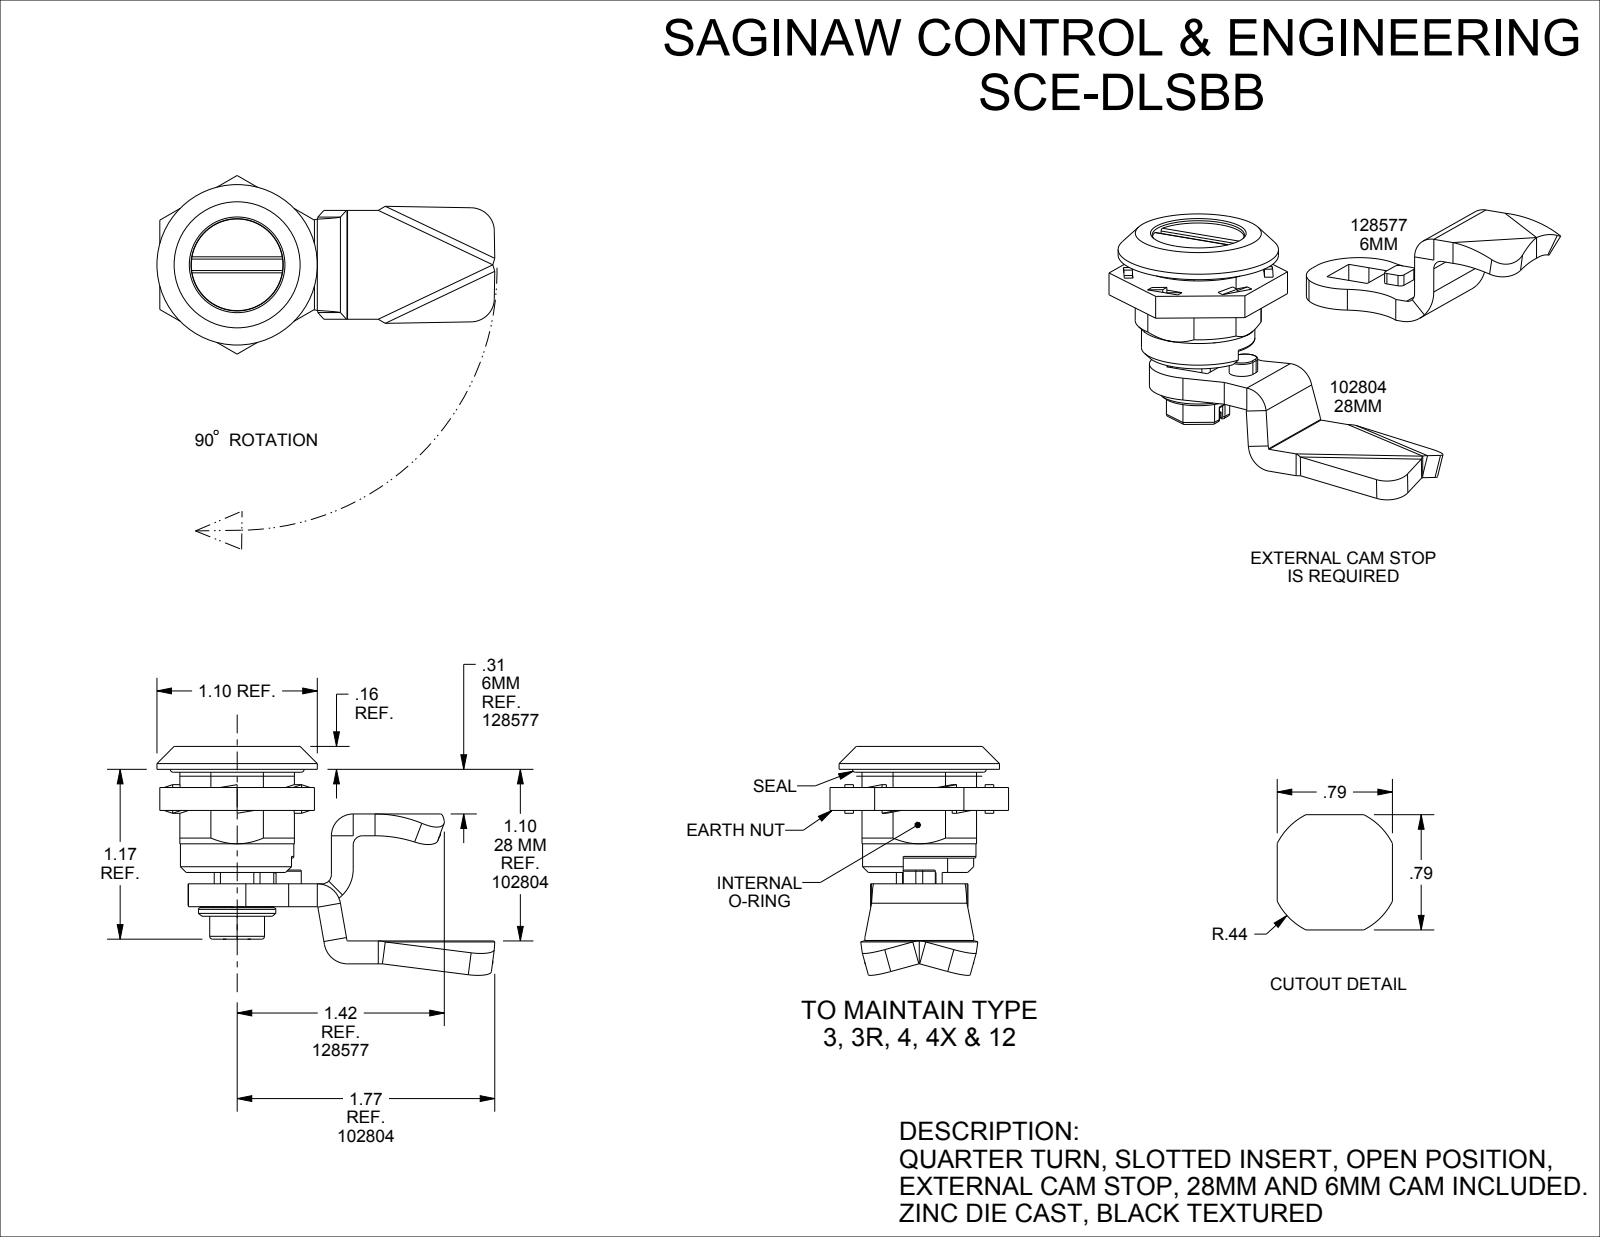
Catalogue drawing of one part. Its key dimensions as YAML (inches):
part_name: "SCE-DLSBB"
step_written_by: "SolidWorks 2021 (AUTOMOTIVE_DESIGN)"
units: inches
bodies: {solids: 8, faces: 366, planar: 187, cylindrical: 116, other: 63}
overall_size: [3.322, 2.322, 2.002]
volume: 1.01
surface_area: 19.36
round_holes:
  - {diameter: 0.197, count: 1}
  - {diameter: 0.315, count: 1}
  - {diameter: 0.394, count: 1}
  - {diameter: 0.634, count: 1}
  - {diameter: 0.795, count: 1}
round_bosses_or_shafts:
  - {diameter: 1.102, count: 1}
  - {diameter: 0.78, count: 1}
  - {diameter: 0.63, count: 1}
  - {diameter: 0.531, count: 1}
  - {diameter: 0.504, count: 1}
  - {diameter: 0.39, count: 1}
  - {diameter: 0.217, count: 1}
partial_cylinders:
  - {radius: 0.012, count: 30}
  - {radius: 0.02, count: 12}
  - {radius: 0.03, count: 4}
  - {radius: 0.157, count: 4}
  - {radius: 0.3, count: 4}
  - {radius: 0.004, count: 2}
  - {radius: 0.008, count: 2}
  - {radius: 0.016, count: 2}
face_to_face_distances: [0.157, 1.054, 0.393, 0.662, 0.15, 1.337, 0.282, 0.944, 0.48, 0.787]
